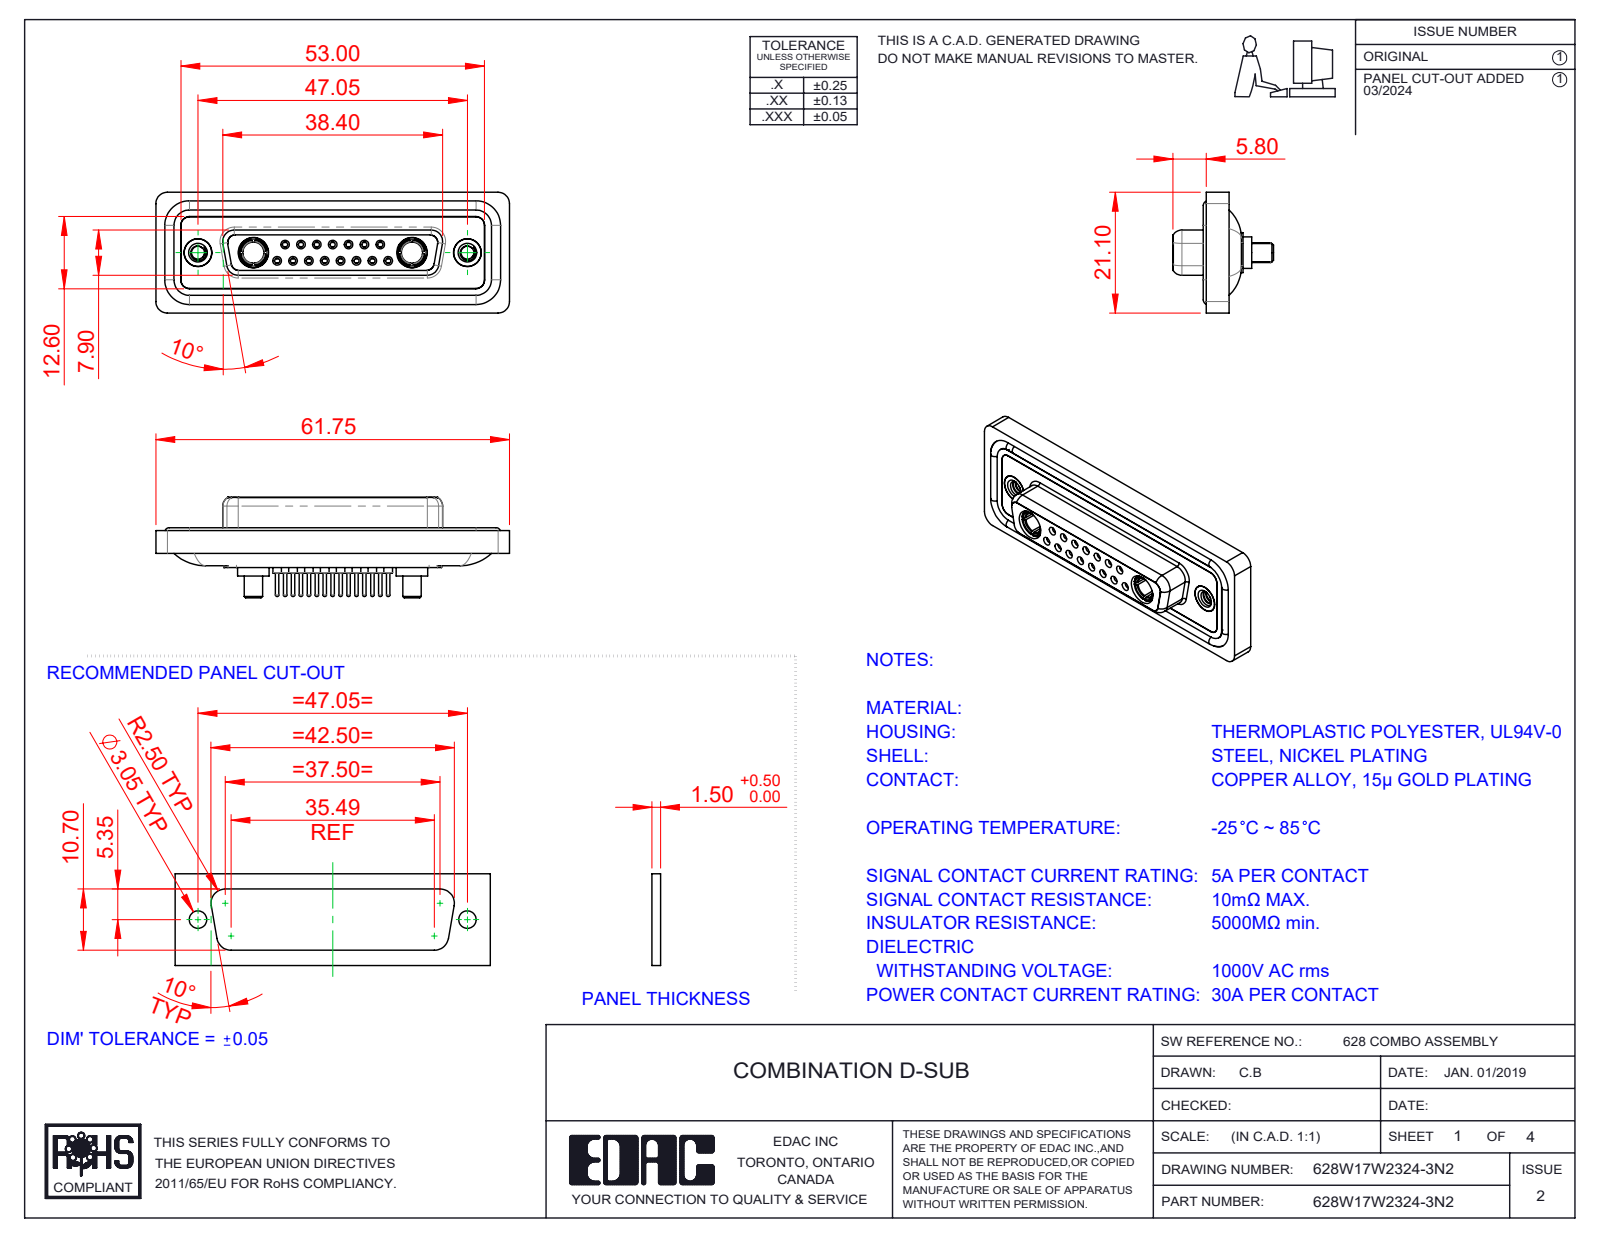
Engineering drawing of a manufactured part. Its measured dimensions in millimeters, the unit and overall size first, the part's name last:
Units: millimetres
Overall size (bounding box): 61.75 × 21.1 × 17.55
Round holes (diameter × count): ⌀0.9 ×15, ⌀1.1 ×15, ⌀1.5 ×15, ⌀2 ×15, ⌀1.6 ×8, ⌀1.7 ×7, ⌀4.85 ×4, ⌀2.26 ×2, ⌀3.7 ×2, ⌀4 ×2, ⌀4.05 ×2, ⌀5 ×2
Round bosses / shafts (diameter × count): ⌀2.2 ×15, ⌀0.6 ×15, ⌀1.6 ×11, ⌀5.5 ×2, ⌀5.2 ×2, ⌀4.96 ×2, ⌀4.95 ×2, ⌀4.8 ×2
Partial cylindrical surfaces — rounded edges, fillets, slot ends (radius × count): R1.5 ×22, R2 ×18, R1.35 ×8, R1.6 ×8, R0.25 ×4, R0.5 ×4, R0.6 ×4, R0.65 ×4
Main face-to-face distances: 0.4, 1.8, 7.45, 5.65, 6.6, 0.5, 7.05, 1.6, 2.9, 1.1
Hole centre spacings: 3.16, 2.77, 8.31, 5.54, 5.03, 5.04, 7.49, 11.08
Volume: 8 338 mm³ · Surface area: 13 864 mm²
Bodies: 26 solids, 1359 faces (388 planar, 519 cylindrical, 452 other)
Part name (STEP PRODUCT): 628Combo Shell Front_25 Contacts; 628Combo Contact Row 1_24; 628Combo Threaded Rivet_2; 628Combo Housing_17W2 (+5 more)
STEP written by: SolidWorks 2023 (CONFIG_CONTROL_DESIGN)
